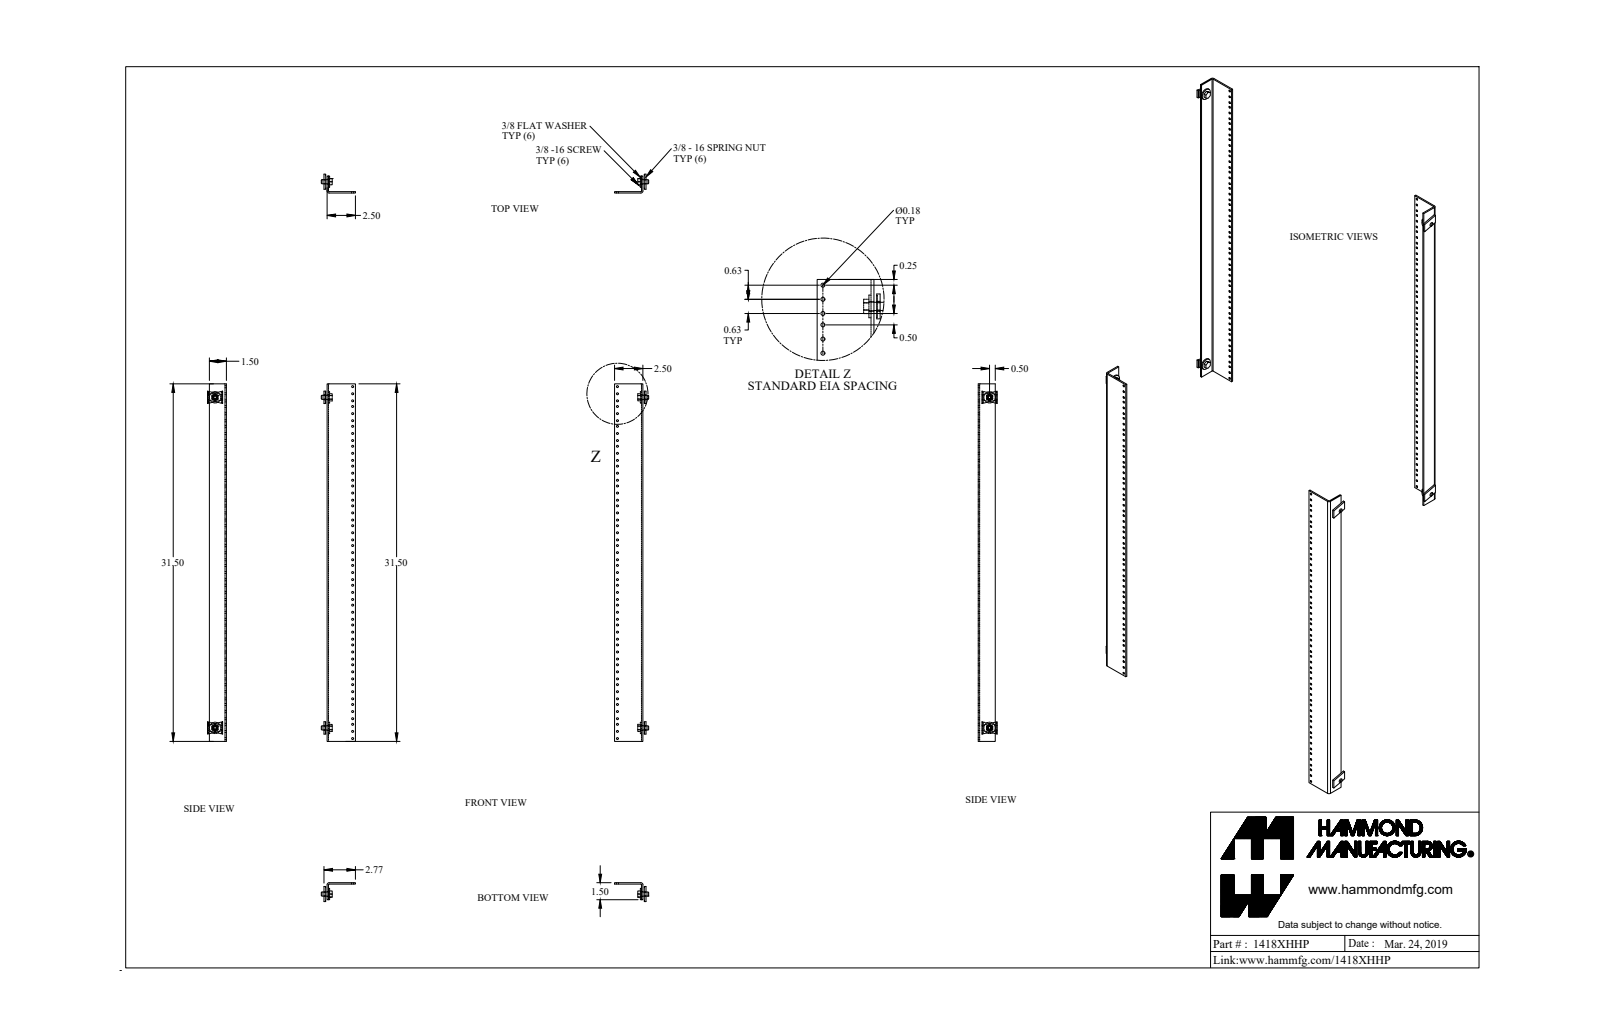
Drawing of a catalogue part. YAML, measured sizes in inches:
part_name: "1418XHHP_Default"
step_written_by: "SolidWorks 2019 (CONFIG_CONTROL_DESIGN)"
units: inches
bodies: {solids: 14, faces: 392, planar: 124, cylindrical: 260, other: 8}
overall_size: [31.5, 28.856, 1.668]
volume: 31.02
surface_area: 525.7
round_holes:
  - {diameter: 0.177, count: 108}
  - {diameter: 0.313, count: 2}
  - {diameter: 0.437, count: 2}
  - {diameter: 0.445, count: 2}
round_bosses_or_shafts:
  - {diameter: 1, count: 2}
  - {diameter: 0.36, count: 2}
partial_cylinders:
  - {radius: 0.06, count: 2}
  - {radius: 0.185, count: 2}
face_to_face_distances: [0.125, 0.125, 27.84, 27.59, 27.715, 27.715, 1.5, 1.375, 1.375, 2.5]
hole_center_spacings: [1.75, 3.5, 5.25, 7, 8.75, 0.5, 1.25, 10.5]
